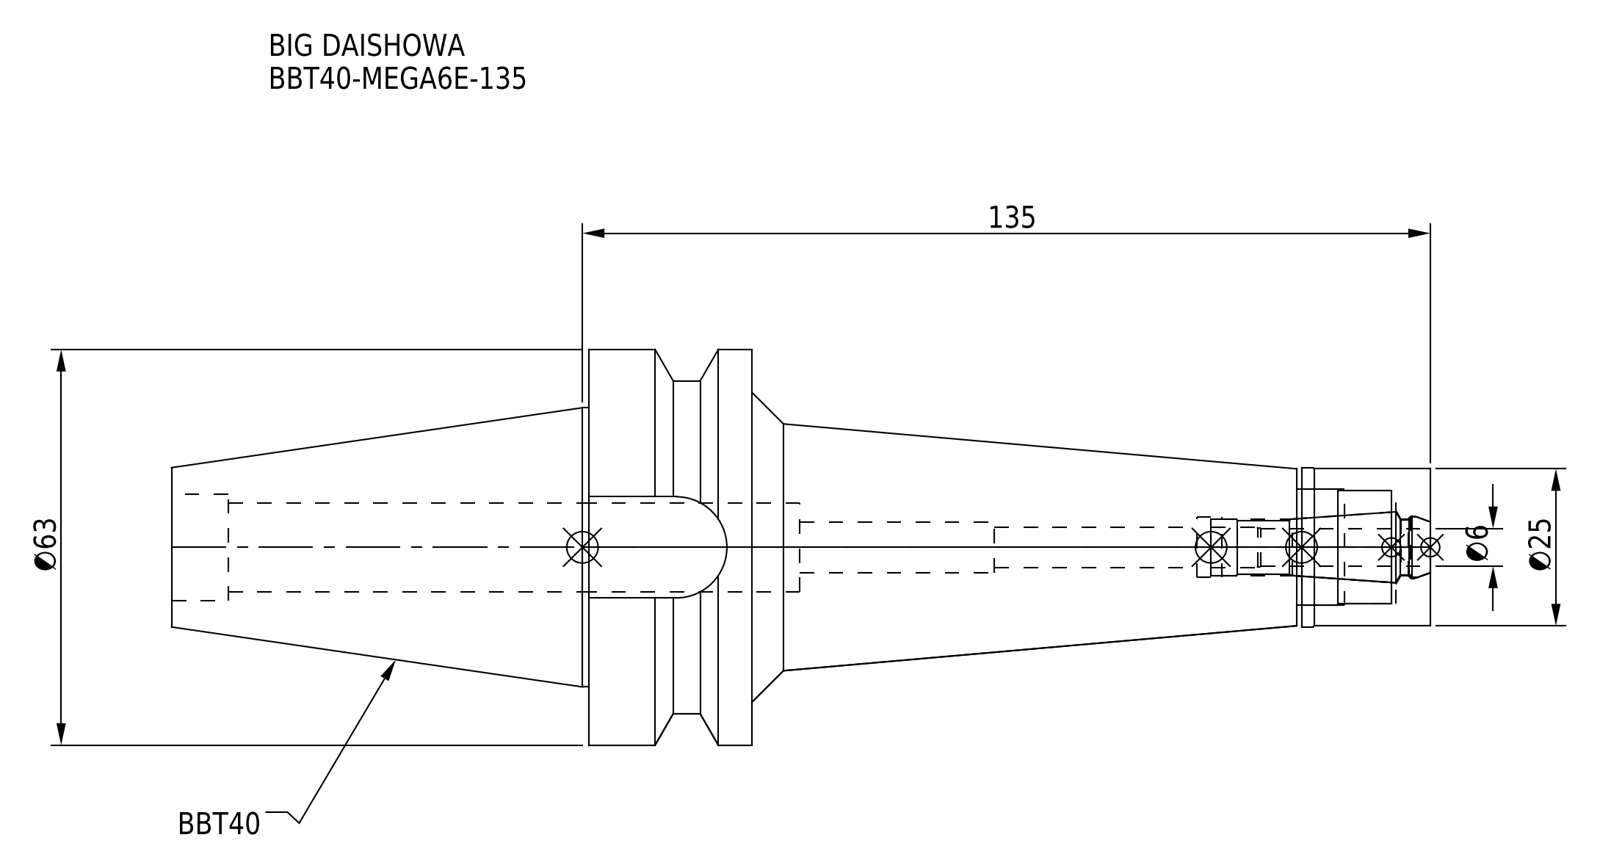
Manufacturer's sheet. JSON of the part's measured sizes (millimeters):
{"part_name": "BBT40-MEGA6E-135-060-FreeParts; DXF_TEMP_ASSY_ASM_4_ASM.stp; BBT40-MEGA6E-135; BBT40ME06135-060_ASM.stp (+3 more)", "step_written_by": "SolidWorks 2019 (CONFIG_CONTROL_DESIGN)", "units": "millimeters", "bodies": {"solids": 2, "faces": 81, "planar": 21, "cylindrical": 40, "other": 20}, "overall_size": [200.4, 63, 63], "volume_mm3": 199135, "surface_area_mm2": 37856, "round_holes": [[6.4, 1], [8, 1], [9, 1], [9.6, 1], [9.9, 1], [14.2, 1], [17, 1], [18, 1], [18.5, 1]], "round_bosses_or_shafts": [[63, 1], [53, 1], [44.45, 1], [25.3, 1], [25, 1]], "partial_cylinders_radius": [[8.05, 1]], "face_to_face_distances": [26, 108, 134, 45, 200.4, 92.4, 66.4, 86.7, 20.5, 87.5]}
